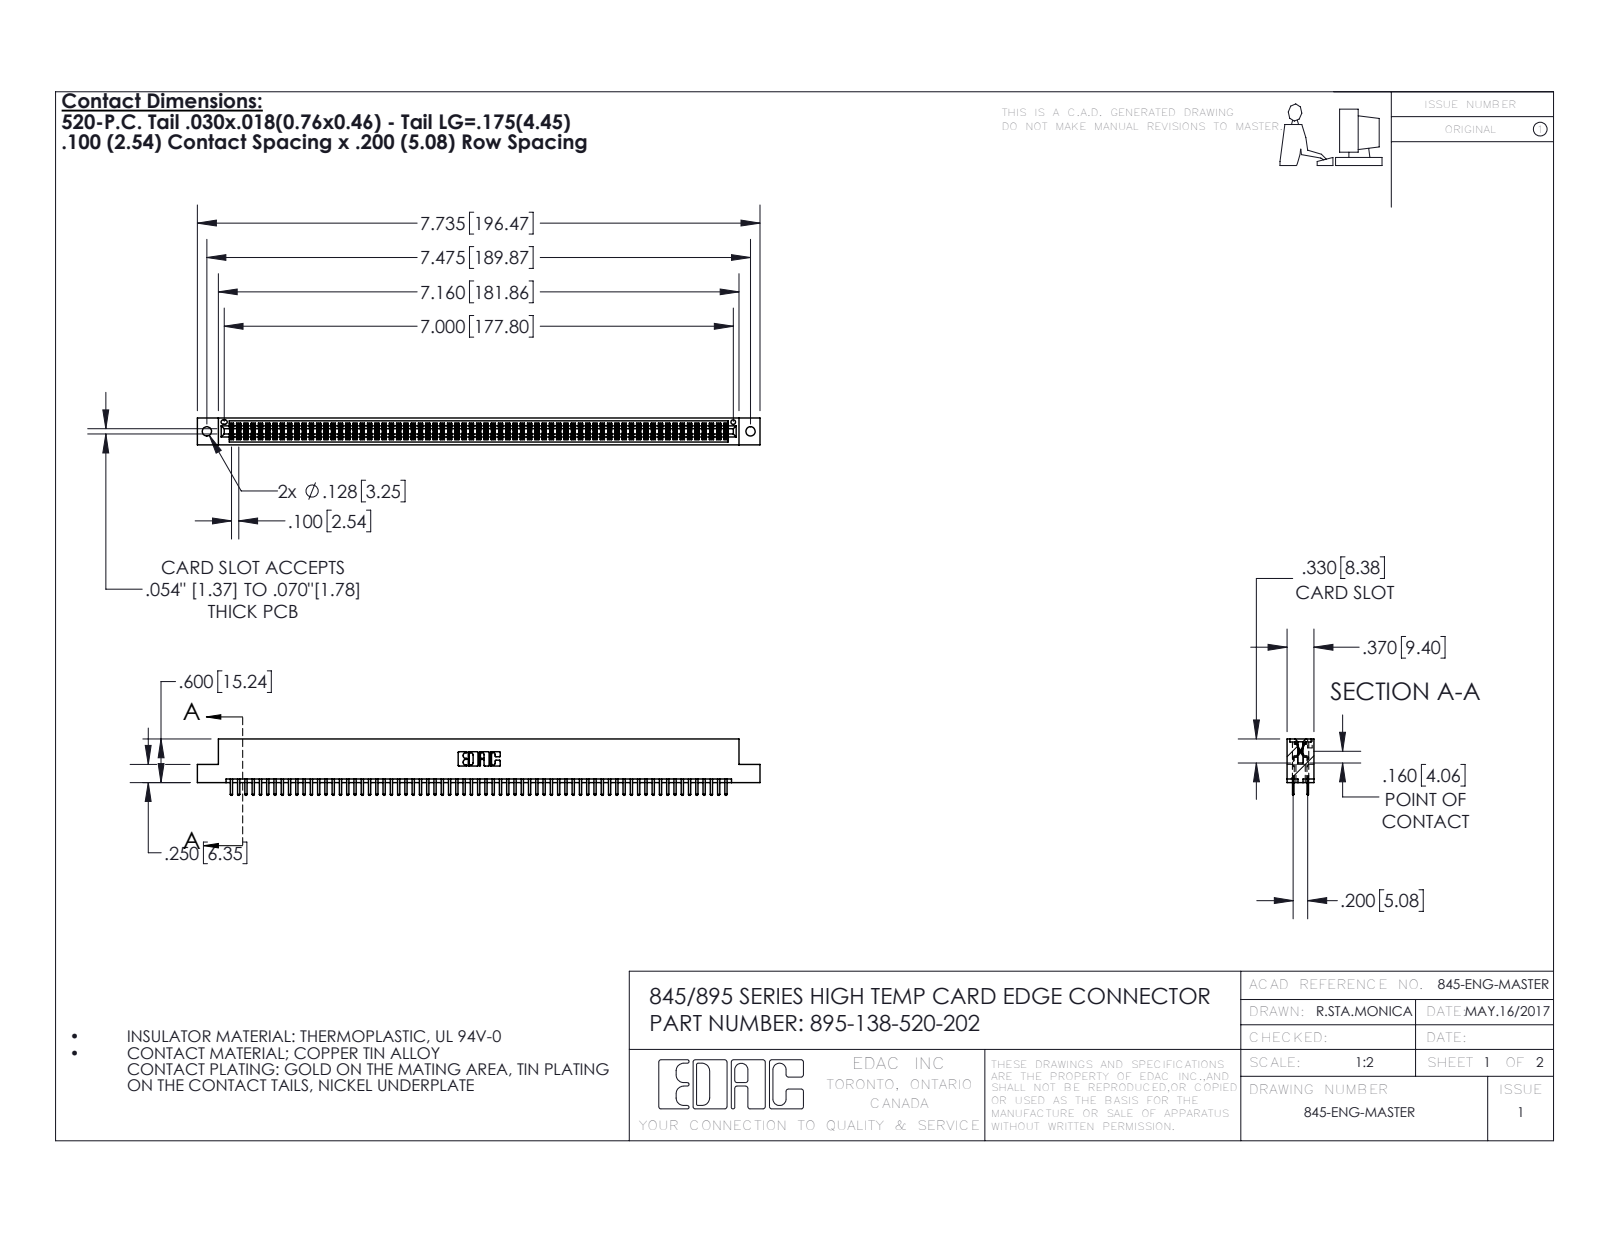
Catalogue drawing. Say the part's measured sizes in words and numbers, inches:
The part is named "345-292-001_345-293-120; 345 Part_Flush Mounting Lugs - 0.128 Dia; 395-138-520-202". Its 3-D file was written by "SolidWorks 2016 (CONFIG_CONTROL_DESIGN)". It is 139 solids with 7578 faces: 4910 planar, 2668 cylindrical and 0 other. Overall it measures 7.735 by 0.775 by 0.37 inches. Its volume is 1.174 cubic inches and its surface area 44.27 square inches. Round holes: 2 of diameter 0.128, 1 of diameter 0.064. Partial cylindrical surfaces (rounded edges, fillets, slot ends): 207 of radius 0.006, 142 of radius 0.01, 22 of radius 0.01, 6 of radius 0.007, 6 of radius 0.031, 3 of radius 0.026, 2 of radius 0.014, 2 of radius 0.019. The main face-to-face distances are 0.298, 0.072, 0.2, 0.37, 0.098, 0.272, 0.025, 0.225, 0.022, 0.072. The hole center spacings are 0.27, 7.239, 7.475.
